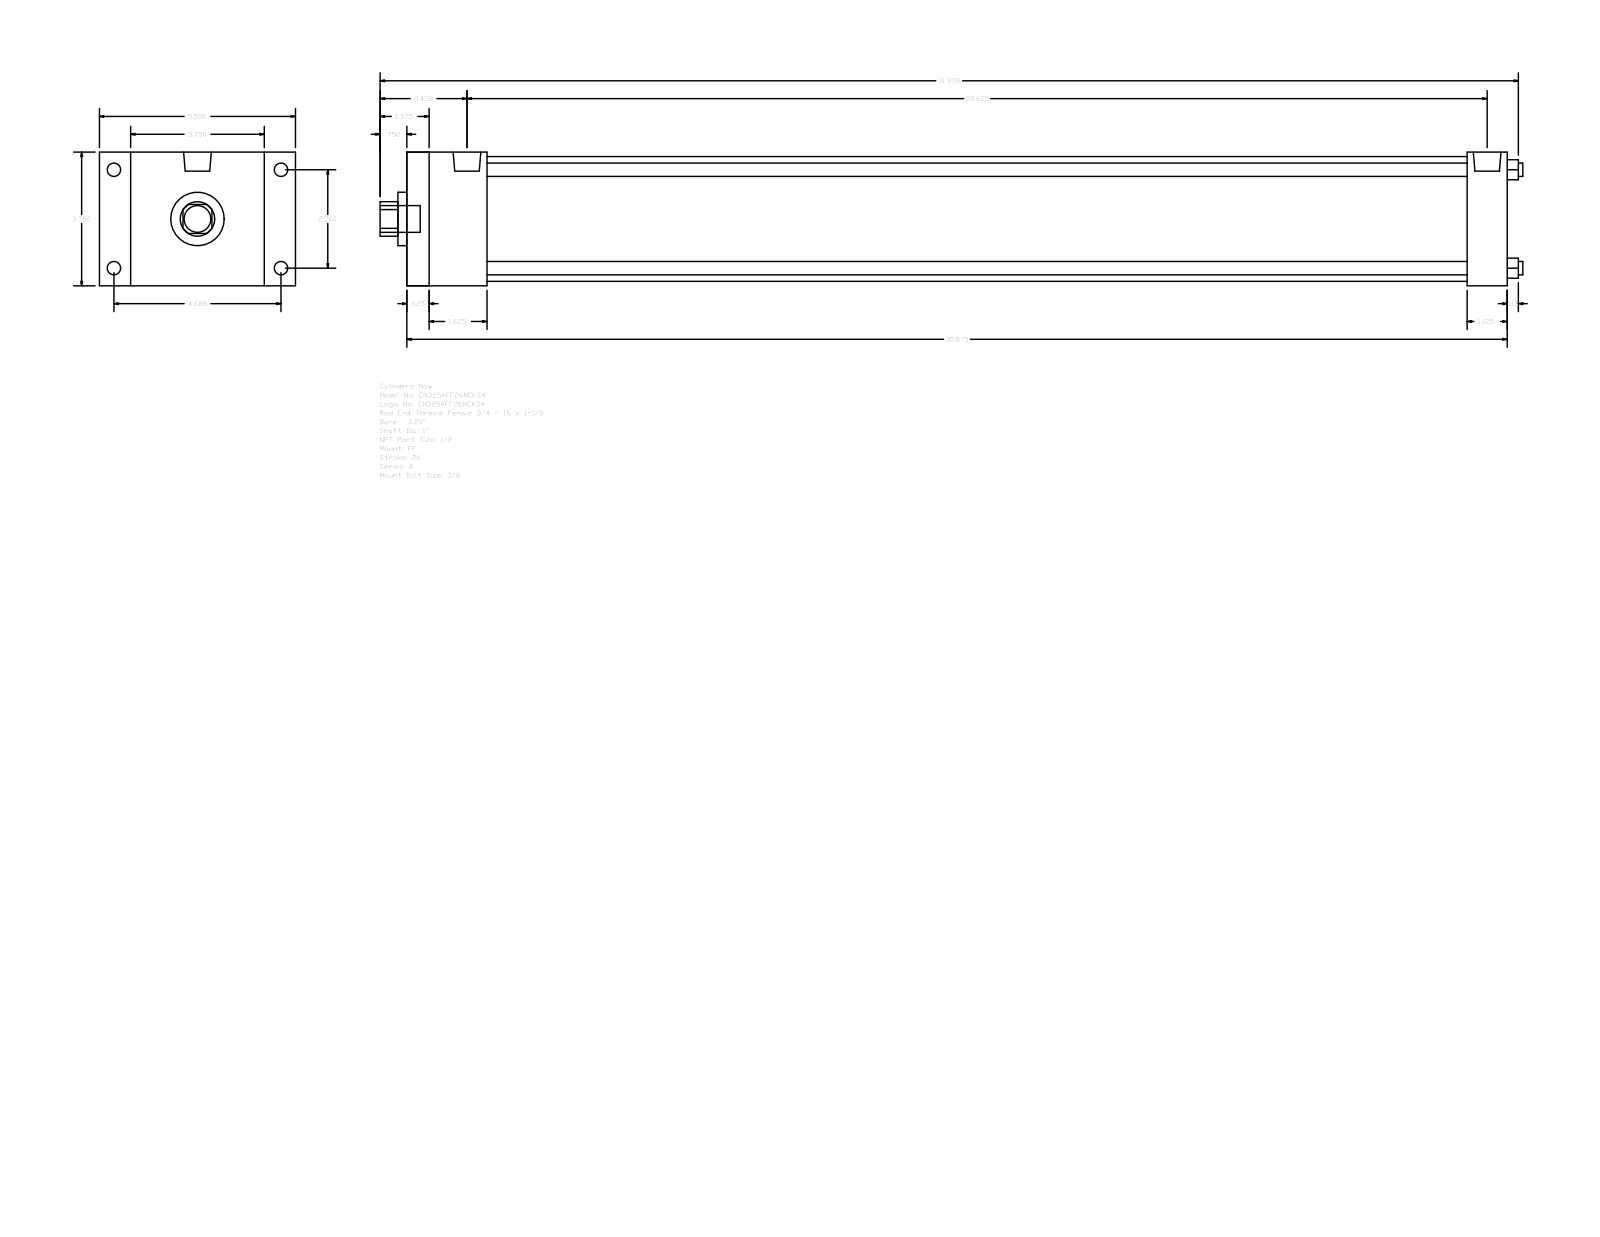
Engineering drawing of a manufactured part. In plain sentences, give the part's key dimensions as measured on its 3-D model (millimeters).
The part is named "A_FF__0325_1". Its 3-D file was written by "GSSL Pune (CONFIG_CONTROL_DESIGN)". It is 0 solids with 92 faces: 64 planar, 28 cylindrical and 0 other. Overall it measures 814.39 by 139.7 by 95.25 millimeters. Round holes: 4 of diameter 9.53, 1 of diameter 25.4, 1 of diameter 38.1, 1 of diameter 88.9. Round bosses or shafts: 4 of diameter 9.53, 4 of diameter 8.73, 2 of diameter 19.77, 1 of diameter 19.05. Partial cylindrical surfaces (rounded edges, fillets, slot ends): 1 of radius 12.29. The main face-to-face distances are 95.24, 784.22, 15.87, 768.35, 22.23, 117.47, 28.57, 57.15, 755.65, 41.28. The hole center spacings are 49.57, 70.1, 99.14.
